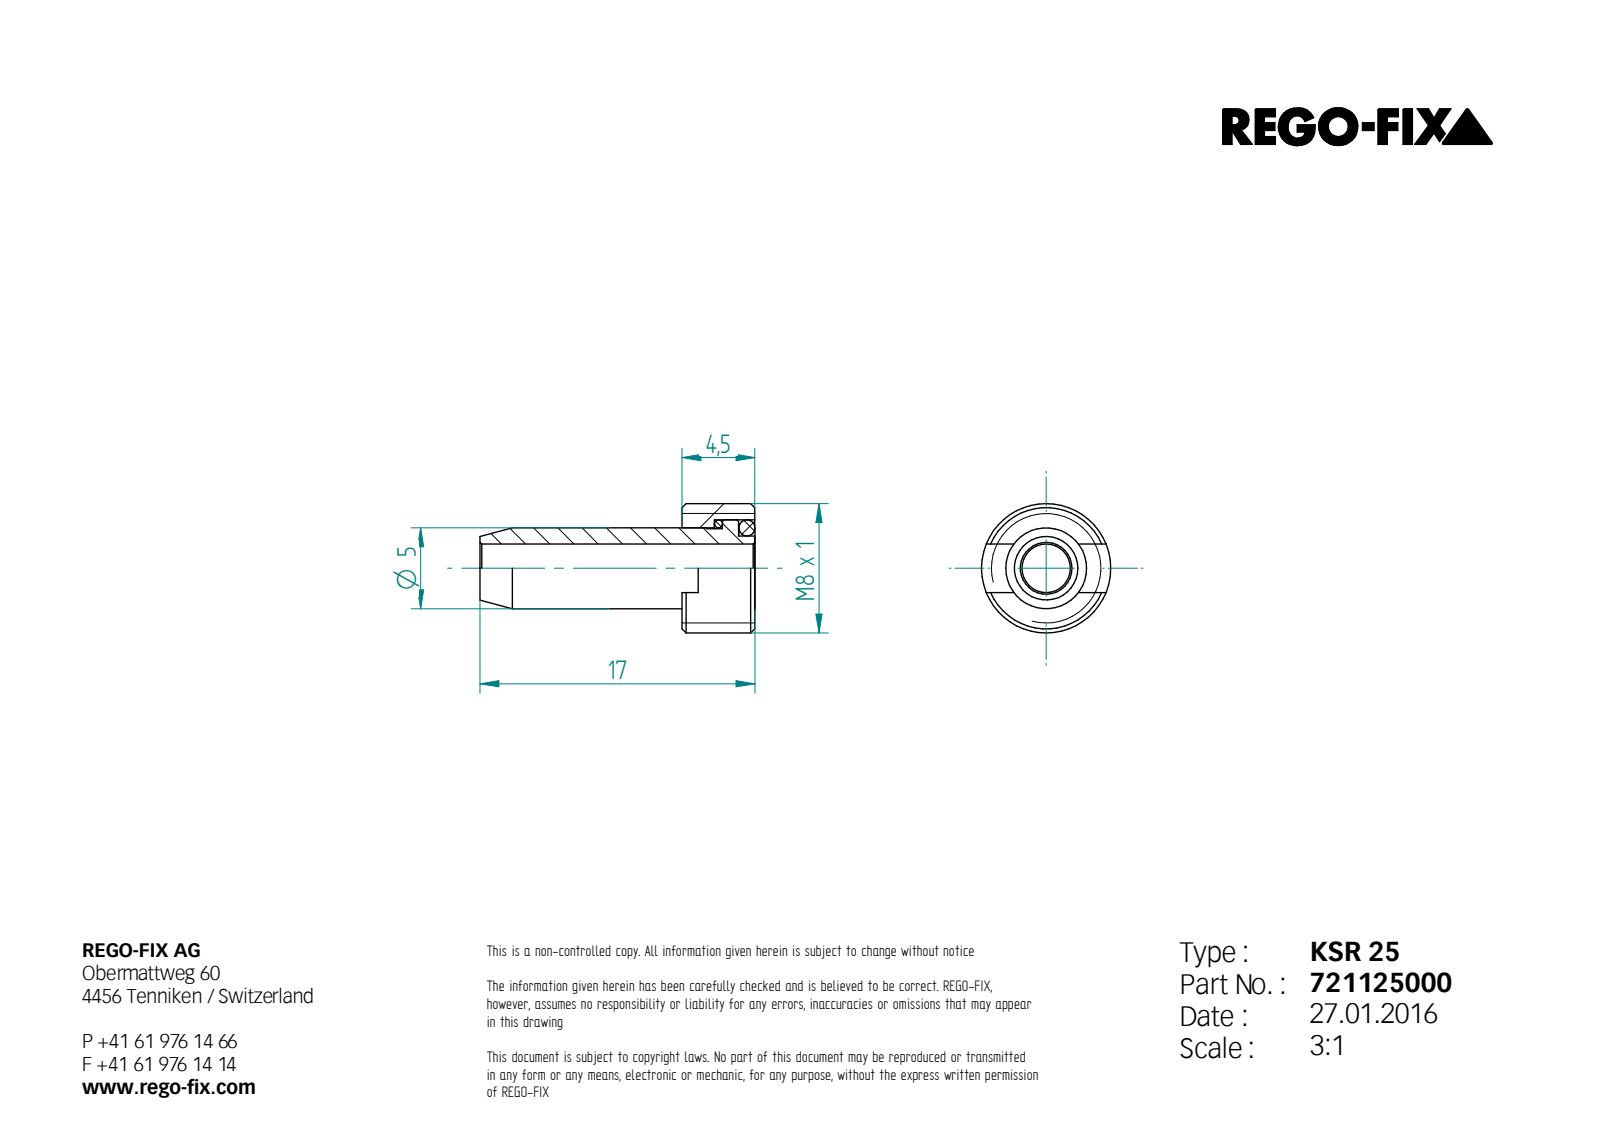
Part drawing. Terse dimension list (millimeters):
name: 0012560; 0012561; 0012563; 0012564
written by: Unknown (AUTOMOTIVE_DESIGN)
unit: mm
bodies: 4 solids, 33 faces (14 planar, 8 cylindrical, 11 other)
size: 17.01 × 8 × 8
volume: 328 mm³; area: 774 mm²
holes: 1× ⌀3, 1× ⌀5, 1× ⌀6
bosses: 1× ⌀8, 1× ⌀4.9, 1× ⌀4
face distances: 1, 2.5, 3.5, 4.5, 2, 1.5, 0.5, 12.5, 13.5, 14.5
